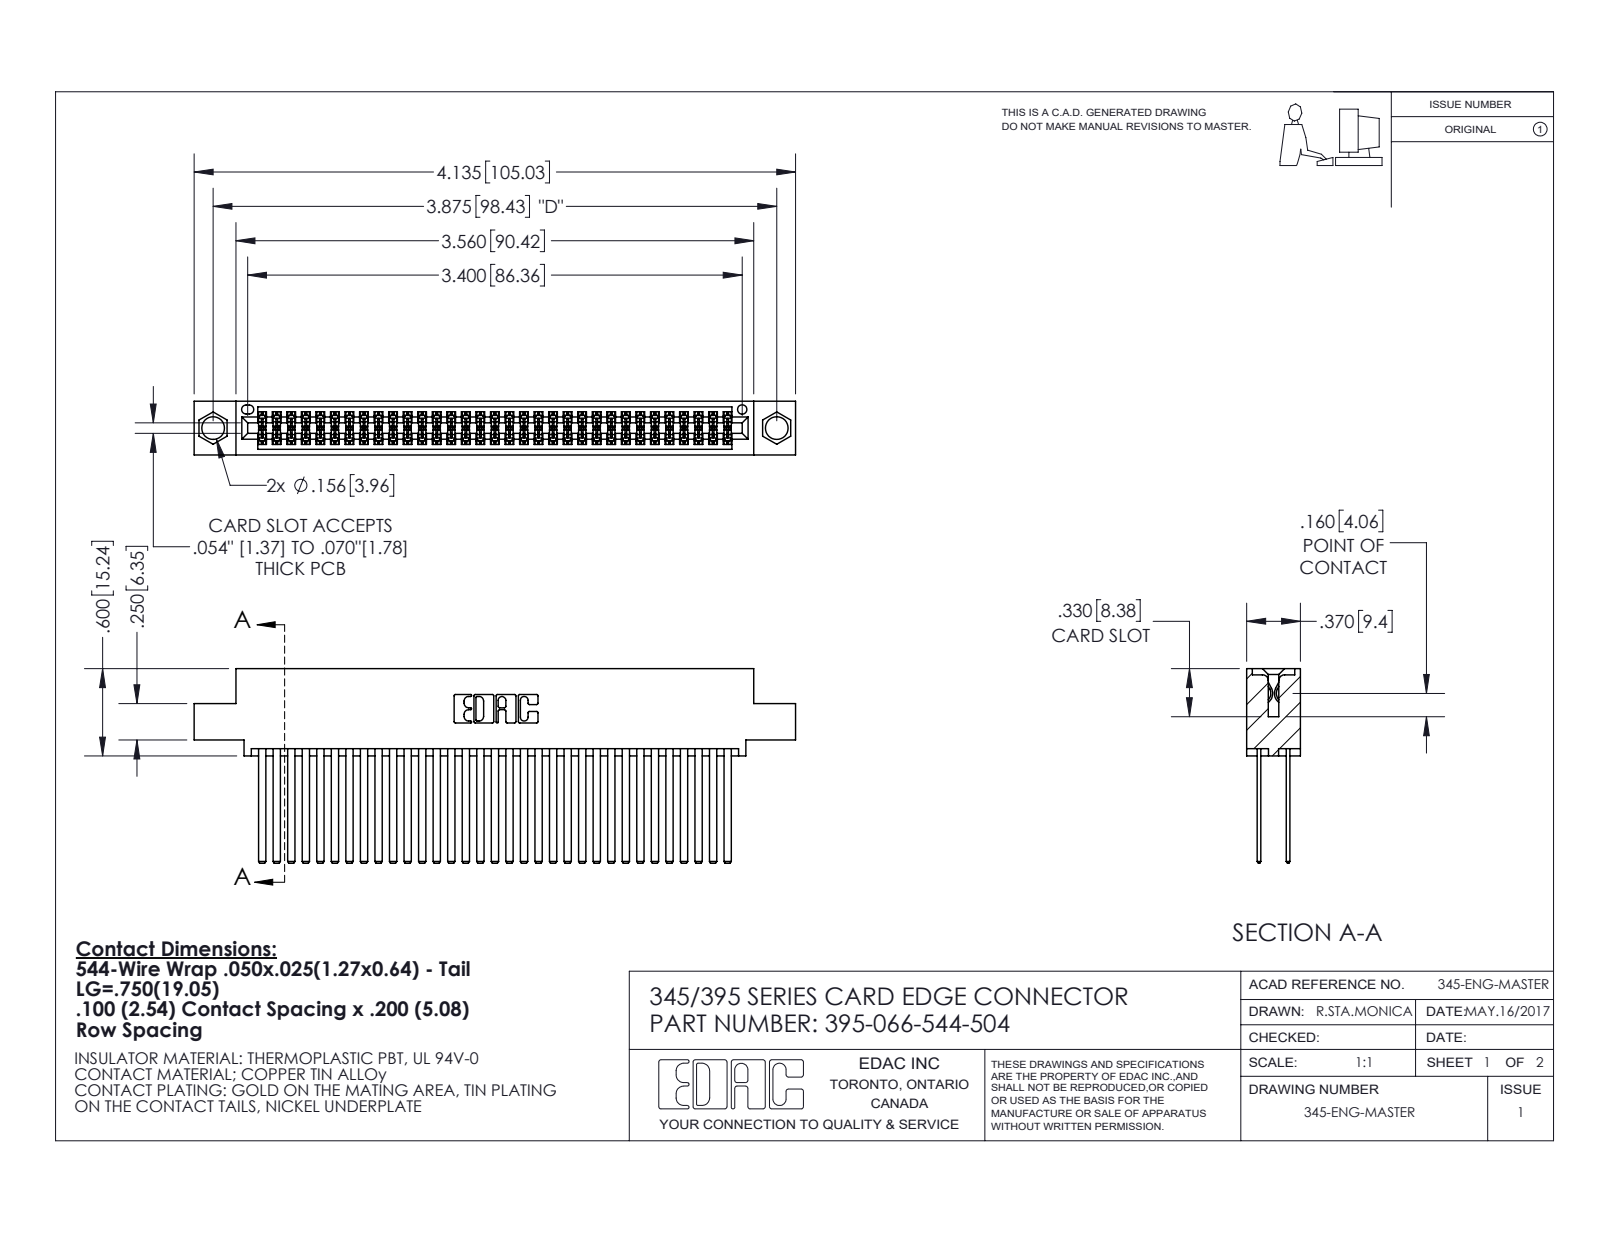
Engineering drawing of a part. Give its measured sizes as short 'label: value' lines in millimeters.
name: 395-066-544-504; 345-292-001_345-293-144; 345 Part_0.110 Offset - 0.156 Dia-TI
written by: SolidWorks 2020 (CONFIG_CONTROL_DESIGN)
unit: mm
bodies: 67 solids, 3048 faces (2012 planar, 1036 cylindrical, 0 other)
size: 105 × 34 × 9.4
volume: 10 900 mm³; area: 18 540 mm²
holes: 2× ⌀4, 1× ⌀1.6
rounds: 132× R0.2, 22× R0.3, 6× R0.2, 6× R0.8, 3× R0.7, 2× R0.4, 2× R0.5, 2× R0.6
face distances: 5.1, 0.6, 1.8, 2.5, 6.9, 7.6, 5.7, 4.4, 9.4, 1.3
hole spacings: 6.9, 92.5, 98.4
